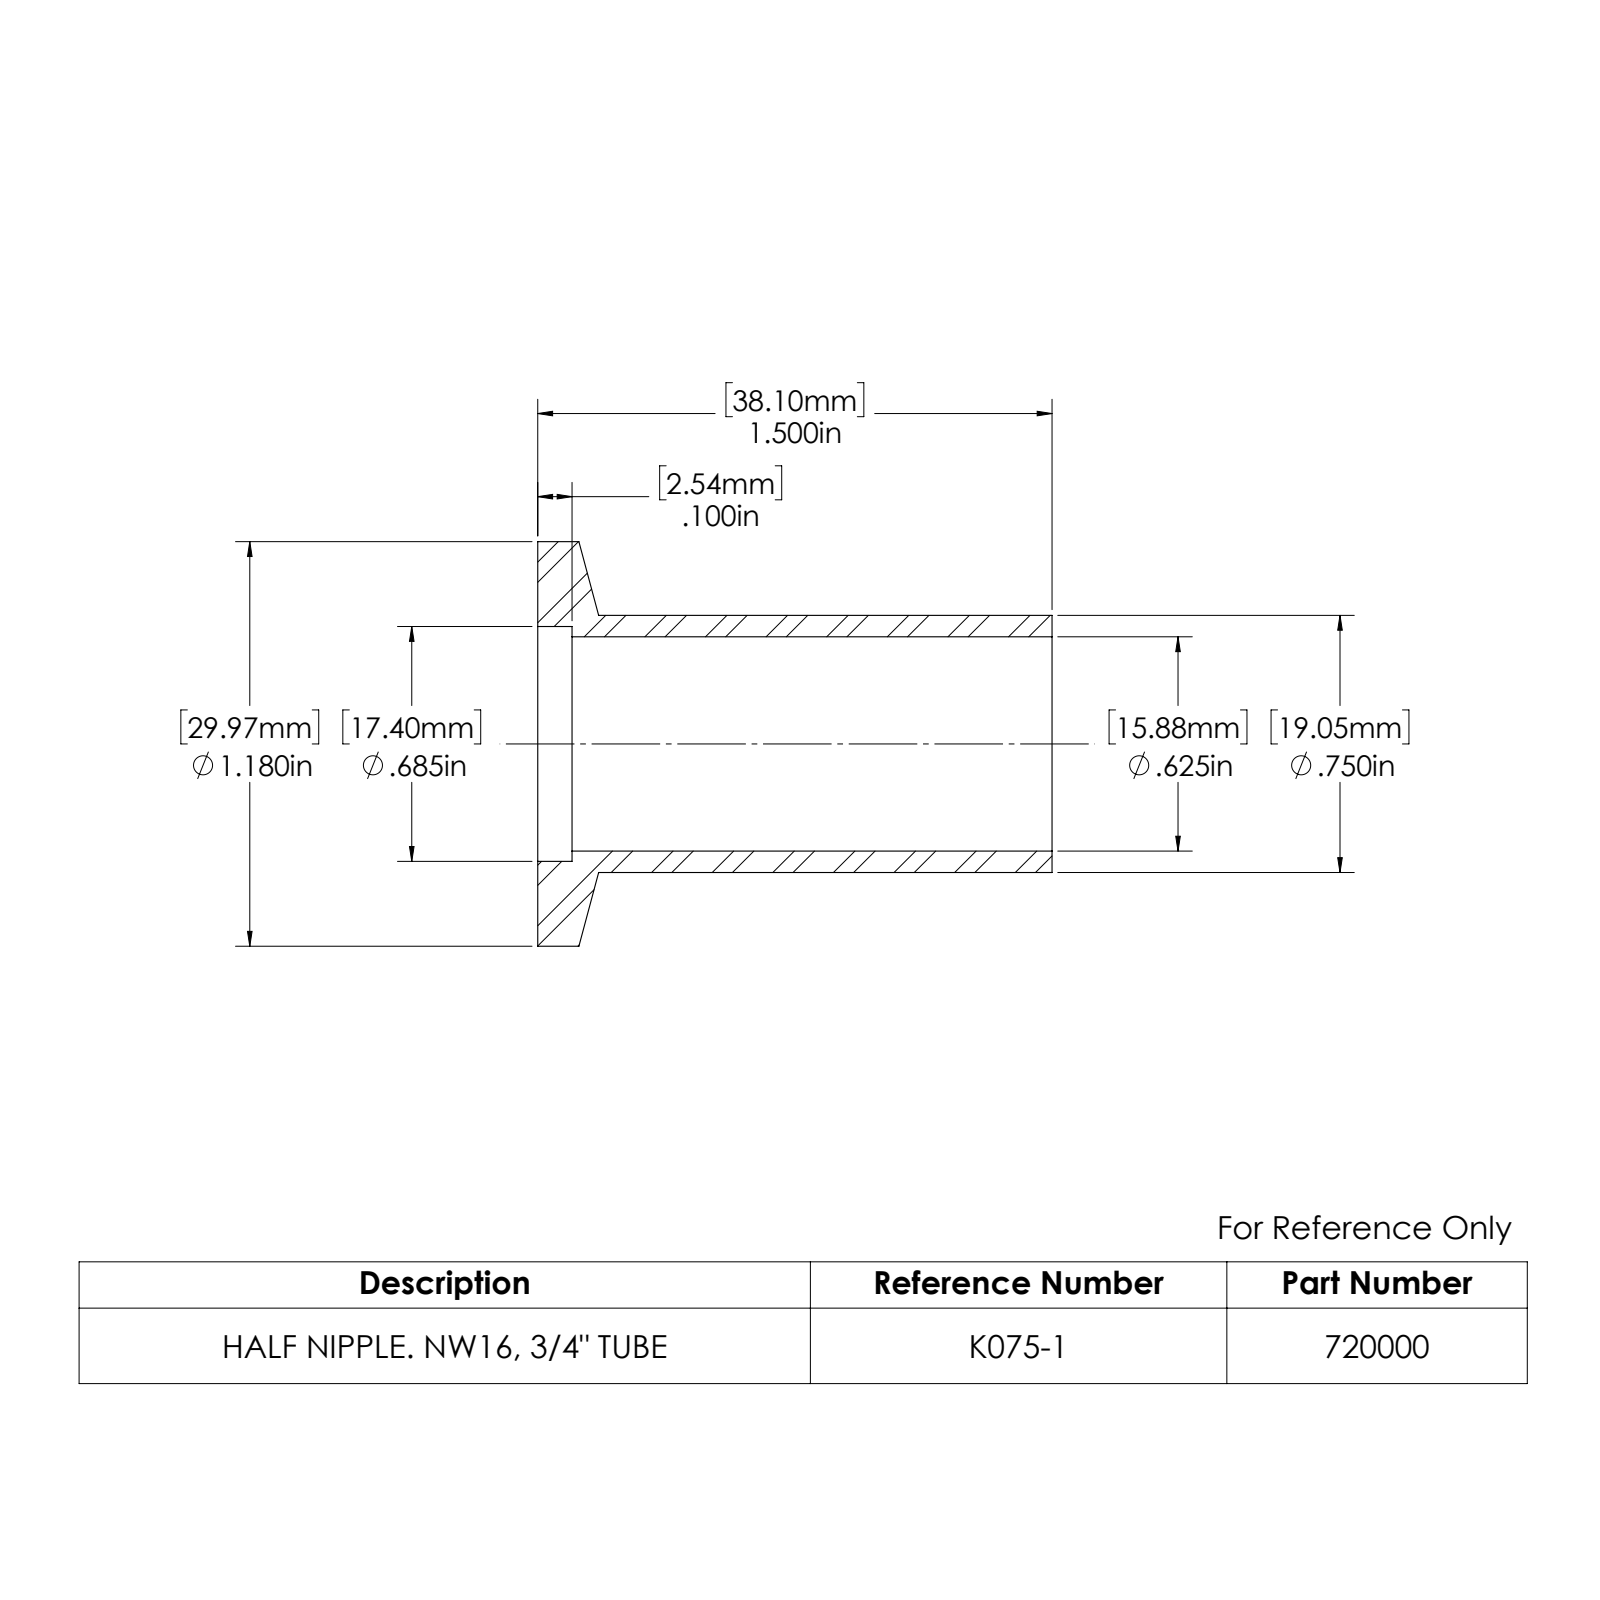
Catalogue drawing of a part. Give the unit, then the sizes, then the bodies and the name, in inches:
Units: inches
Overall size (bounding box): 1.5 × 1.18 × 1.18
Round holes (diameter × count): ⌀0.625 ×1, ⌀0.685 ×1
Round bosses / shafts (diameter × count): ⌀1.18 ×1, ⌀0.75 ×1
Main face-to-face distances: 1.5, 0.1, 1.4
Volume: 0.292 in³ · Surface area: 8.121 in²
Bodies: 1 solid, 13 faces (3 planar, 8 cylindrical, 2 other)
Part name (STEP PRODUCT): 720000
STEP written by: SolidWorks 2022 (AUTOMOTIVE_DESIGN)
